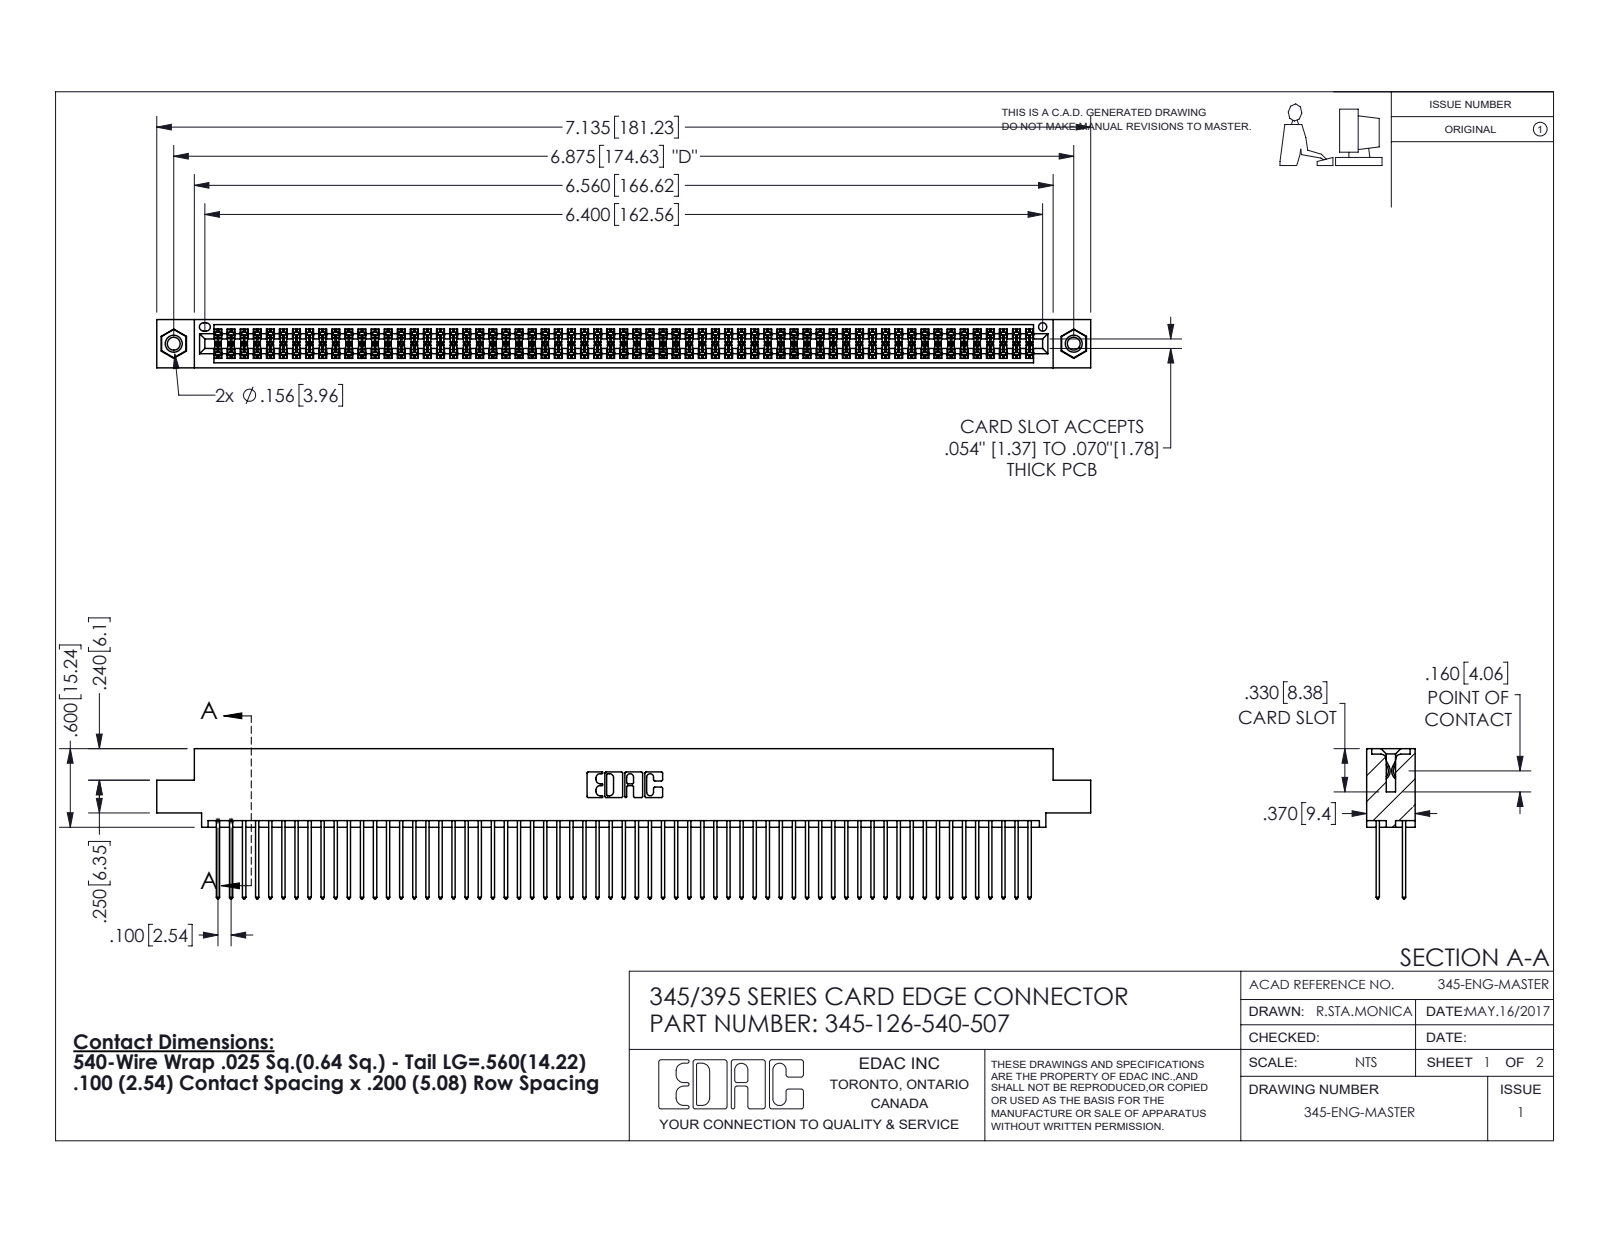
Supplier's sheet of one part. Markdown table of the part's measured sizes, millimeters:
| quantity | value |
| --- | --- |
| part name | 345-292-001_345-293-140; 345-126-540-507; 345-250-001_345-250-005-103; 345 Part_0.110 Offset - 0.156 Dia-TI |
| STEP written by | SolidWorks 2016 (CONFIG_CONTROL_DESIGN) |
| units | millimeters |
| bodies | 129 solids, 6490 faces (4274 planar, 2200 cylindrical, 16 other) |
| overall size | 181.2 × 29.1 × 9.4 |
| volume | 18 190 mm³ |
| surface area | 29 630 mm² |
| round holes (diameter × count) | 2.5 × 2, 3.2 × 2, 4 × 2, 1.6 × 1 |
| round bosses / shafts (diameter × count) | 3.9 × 2 |
| partial cylindrical surfaces (radius × count) | 0.2 × 189, 0.3 × 126, 0.3 × 22, 0.2 × 6, 0.8 × 6, 0.7 × 3, 0.4 × 2, 0.5 × 2 |
| main face-to-face distances | 1.8, 7.6, 5.1, 2.5, 6.9, 0.6, 5.7, 9.4, 4.4, 3.8 |
| hole center spacings | 6.9, 168.6, 174.6 |
